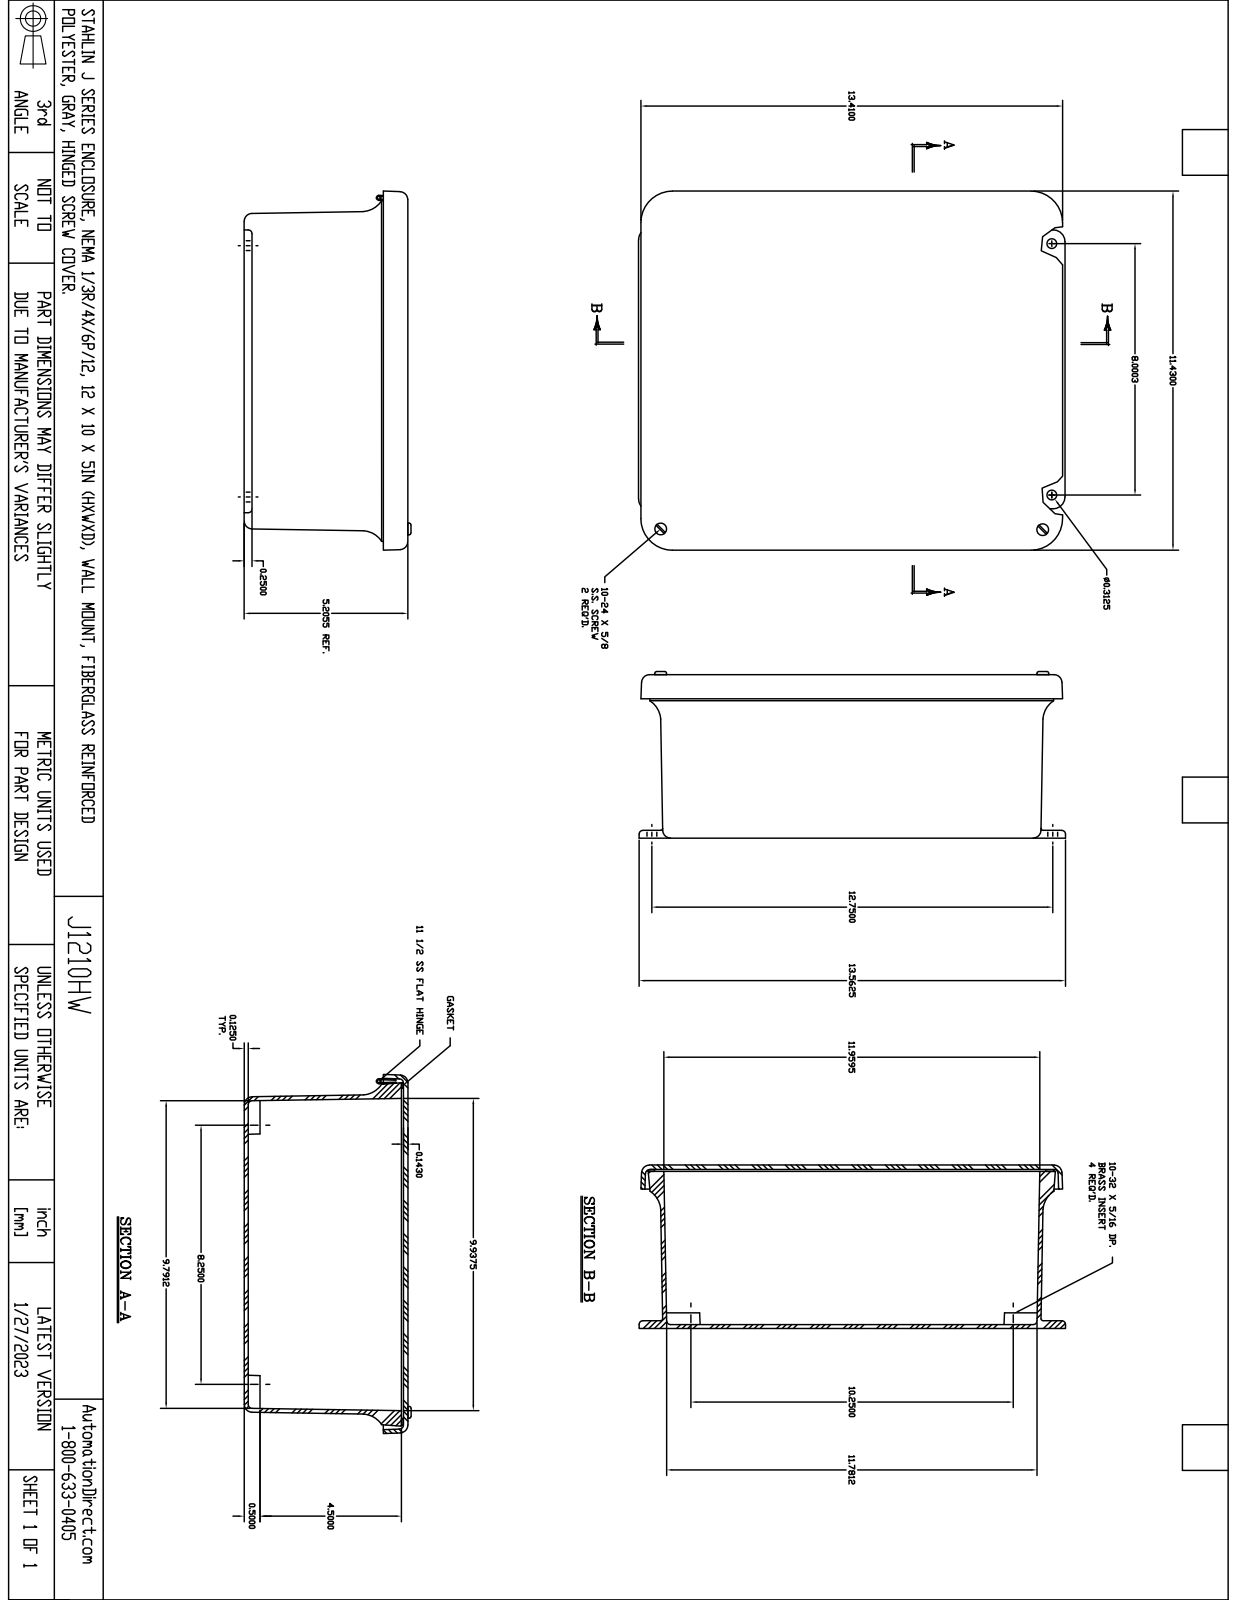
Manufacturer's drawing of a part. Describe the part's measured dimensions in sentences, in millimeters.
The part is named "M1210HW". Its 3-D file was written by "SolidWorks 2018 (AUTOMOTIVE_DESIGN)". It is 22 solids with 799 faces: 283 planar, 307 cylindrical and 209 other. Overall it measures 344.5 by 291.1 by 136.2 millimeters. Its volume is 1 419 000 cubic millimeters and its surface area 752 300 square millimeters. Round holes: 8 of diameter 3.3, 8 of diameter 3.6, 5 of diameter 3.9, 4 of diameter 4, 4 of diameter 5.5, 2 of diameter 3.7, 1 of diameter 2.2. Round bosses or shafts: 8 of diameter 6.4, 6 of diameter 6.9, 5 of diameter 3.2, 3 of diameter 3.2, 2 of diameter 4.8, 2 of diameter 4, 1 of diameter 3.9, 1 of diameter 3.9. Partial cylindrical surfaces (rounded edges, fillets, slot ends): 20 of radius 0.8, 12 of radius 3.2, 8 of radius 6.4, 7 of radius 5.1, 4 of radius 9.5, 4 of radius 19.1, 2 of radius 1.6. The main face-to-face distances are 3.6, 129.3, 132.9, 3.2, 126.1, 129.7, 3.2, 127, 123.8, 5.9. The hole center spacings are 92.1, 92.1, 368.2, 6.4, 34.2, 82.6, 95.3, 174.6.
